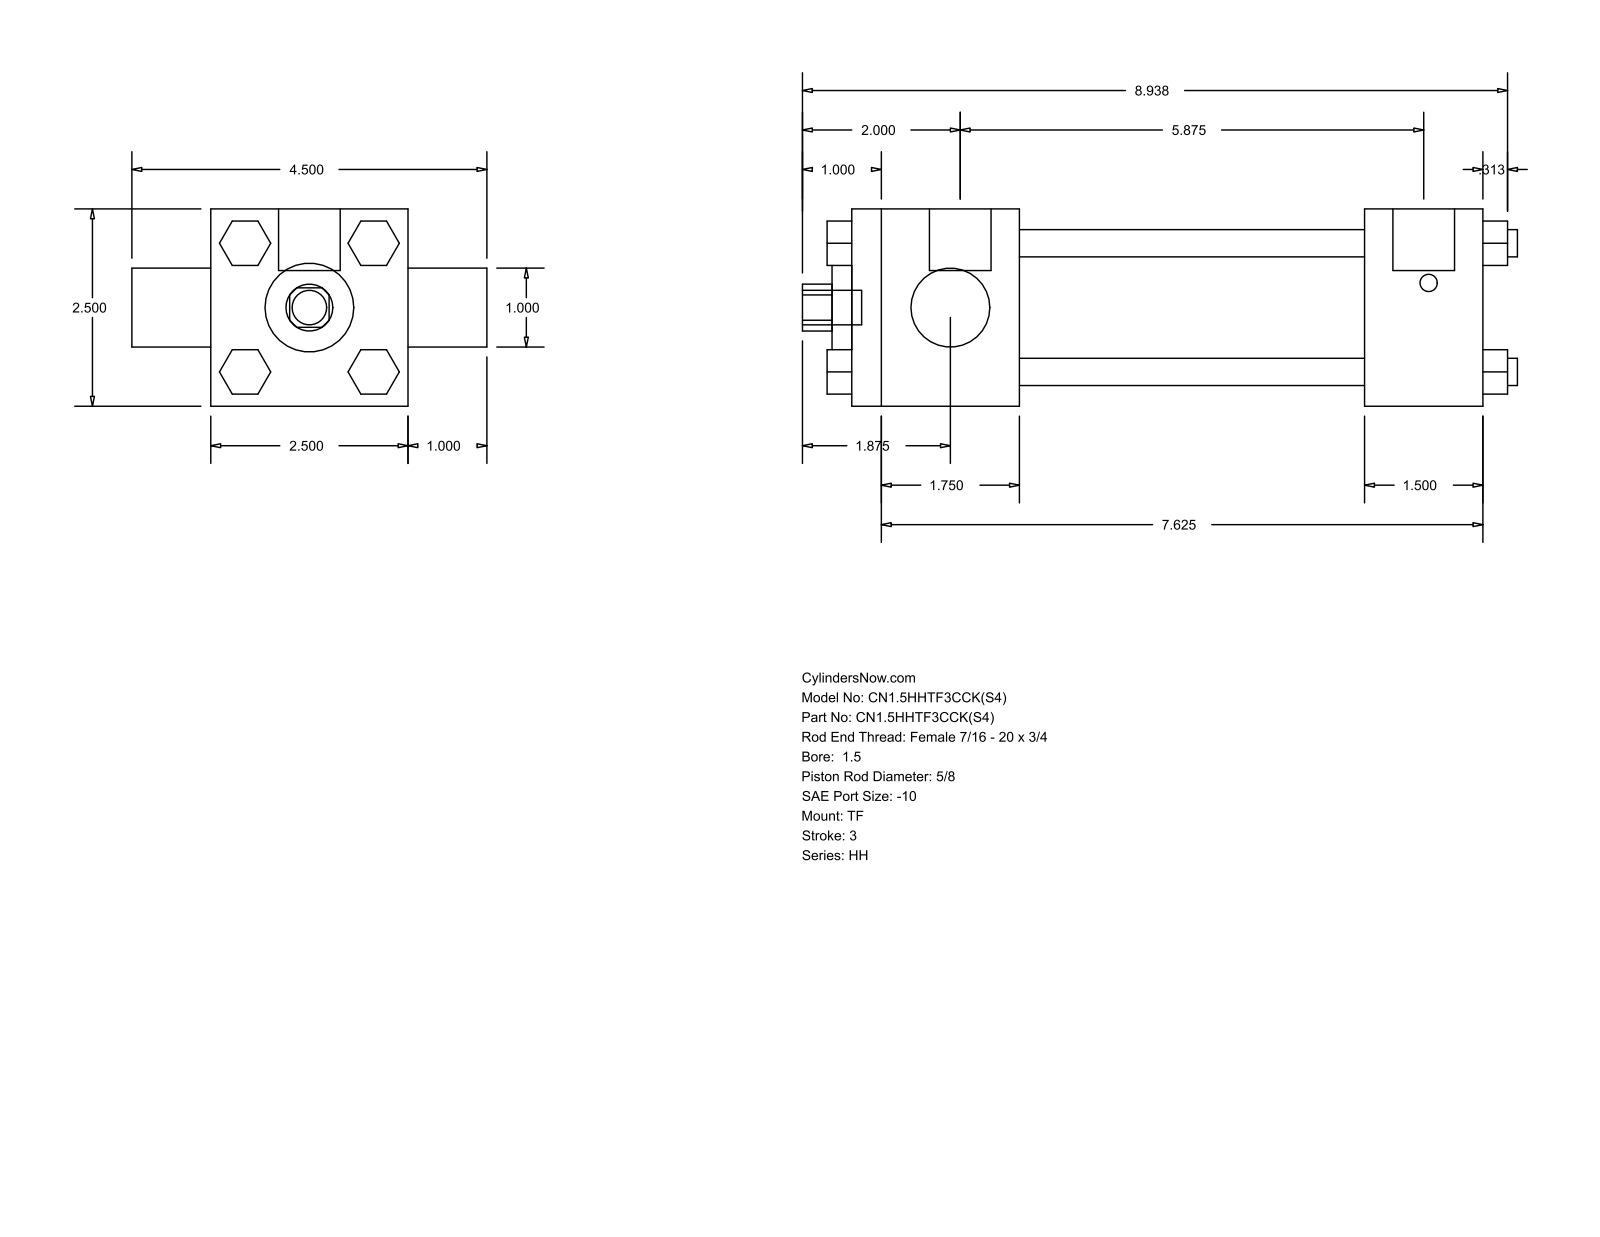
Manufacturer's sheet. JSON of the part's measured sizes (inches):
{"part_name": "HH_TF__0150_0.625", "step_written_by": "GSSL Pune (CONFIG_CONTROL_DESIGN)", "units": "inches", "bodies": {"solids": 0, "faces": 120, "planar": 92, "cylindrical": 28, "other": 0}, "overall_size": [9.063, 4.5, 2.5], "round_holes": [[0.625, 1], [1, 1], [1.125, 1], [1.75, 1]], "round_bosses_or_shafts": [[0.345, 4], [0.219, 3], [0.781, 2], [0.437, 1]], "partial_cylinders_radius": [[0.297, 1]], "face_to_face_distances": [2.5, 8, 1.5, 2.125, 5.875, 6.5, 4.375, 1, 0.815, 0.563]}
